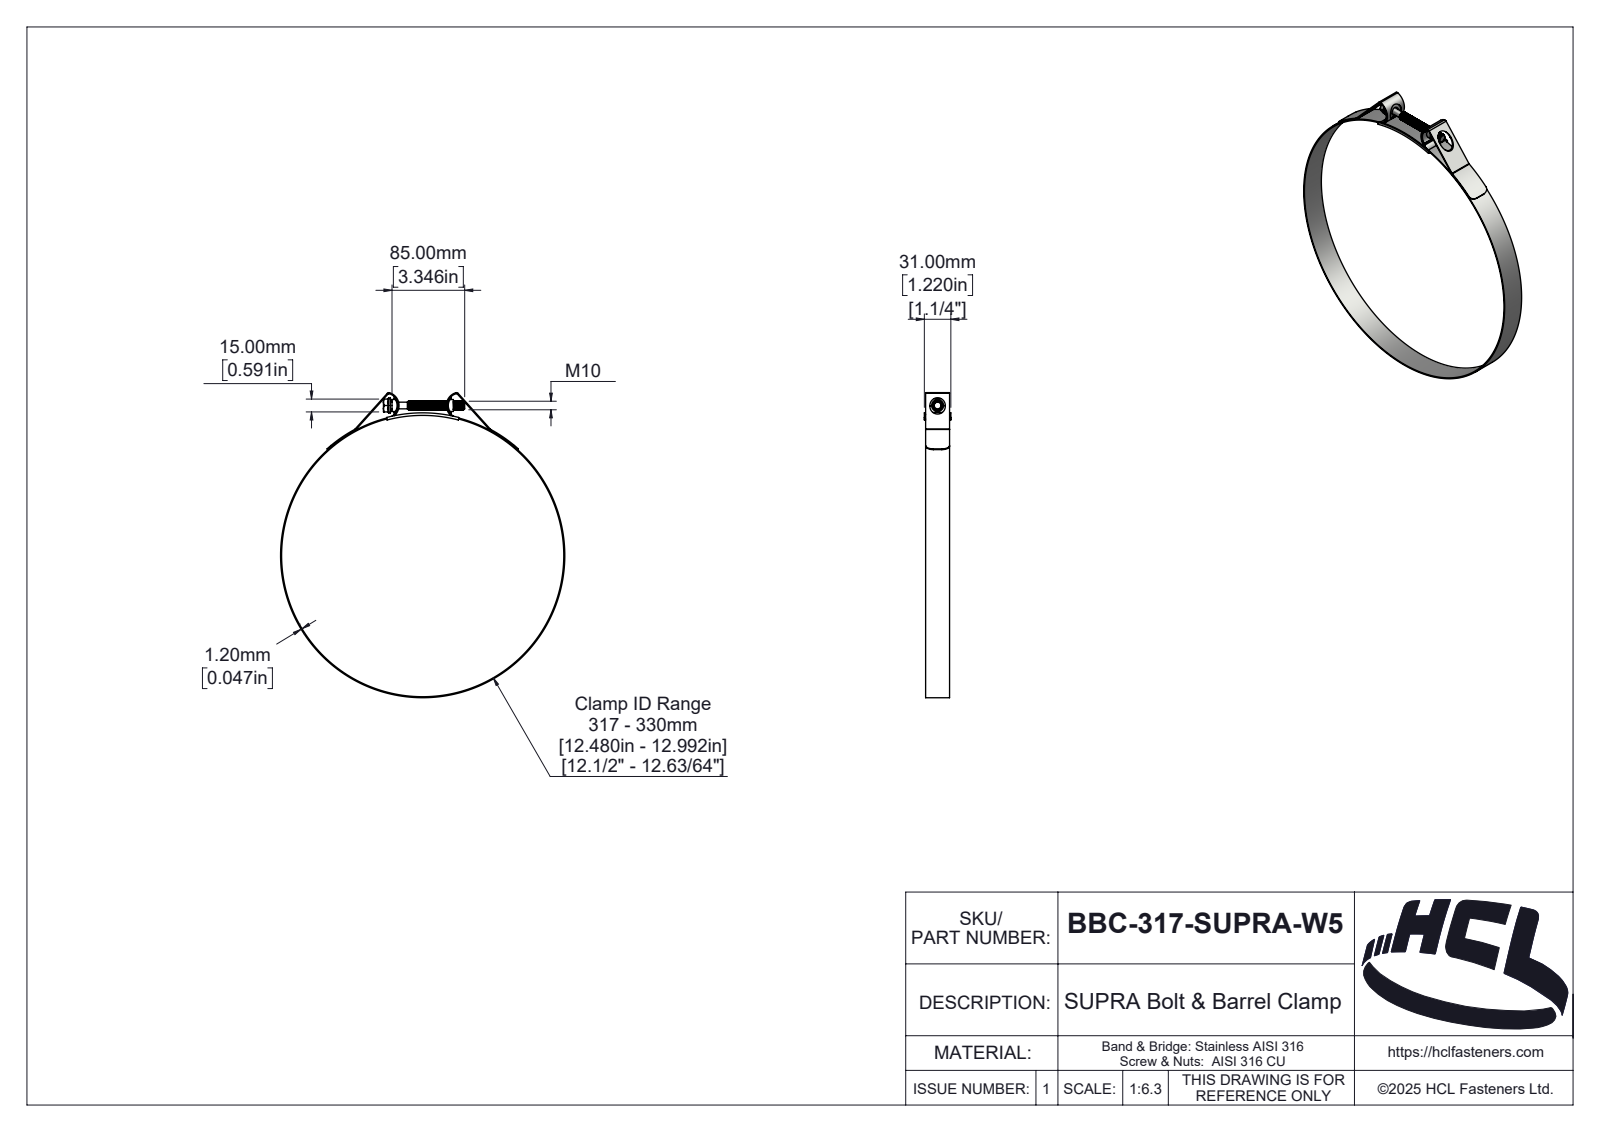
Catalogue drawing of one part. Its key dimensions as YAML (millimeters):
part_name: "BBC-317-SUPRA-W5"
step_written_by: "SolidWorks 2025 (AUTOMOTIVE_DESIGN)"
units: millimeters
bodies: {solids: 5, faces: 380, planar: 50, cylindrical: 243, other: 87}
overall_size: [356.62, 332.4, 31]
volume: 52760
surface_area: 83714
round_holes:
  - {diameter: 330, count: 1}
round_bosses_or_shafts:
  - {diameter: 332.4, count: 1}
  - {diameter: 17.32, count: 1}
  - {diameter: 14, count: 1}
  - {diameter: 10, count: 1}
  - {diameter: 7.8, count: 1}
partial_cylinders:
  - {radius: 1, count: 4}
  - {radius: 1.3, count: 2}
  - {radius: 2, count: 2}
  - {radius: 2.5, count: 2}
  - {radius: 3.2, count: 2}
  - {radius: 9, count: 2}
  - {radius: 13.31, count: 2}
  - {radius: 14.31, count: 2}
face_to_face_distances: [1.2, 28, 1.5, 29.5, 29.8, 28.3, 31, 28.6, 15, 2.5]
